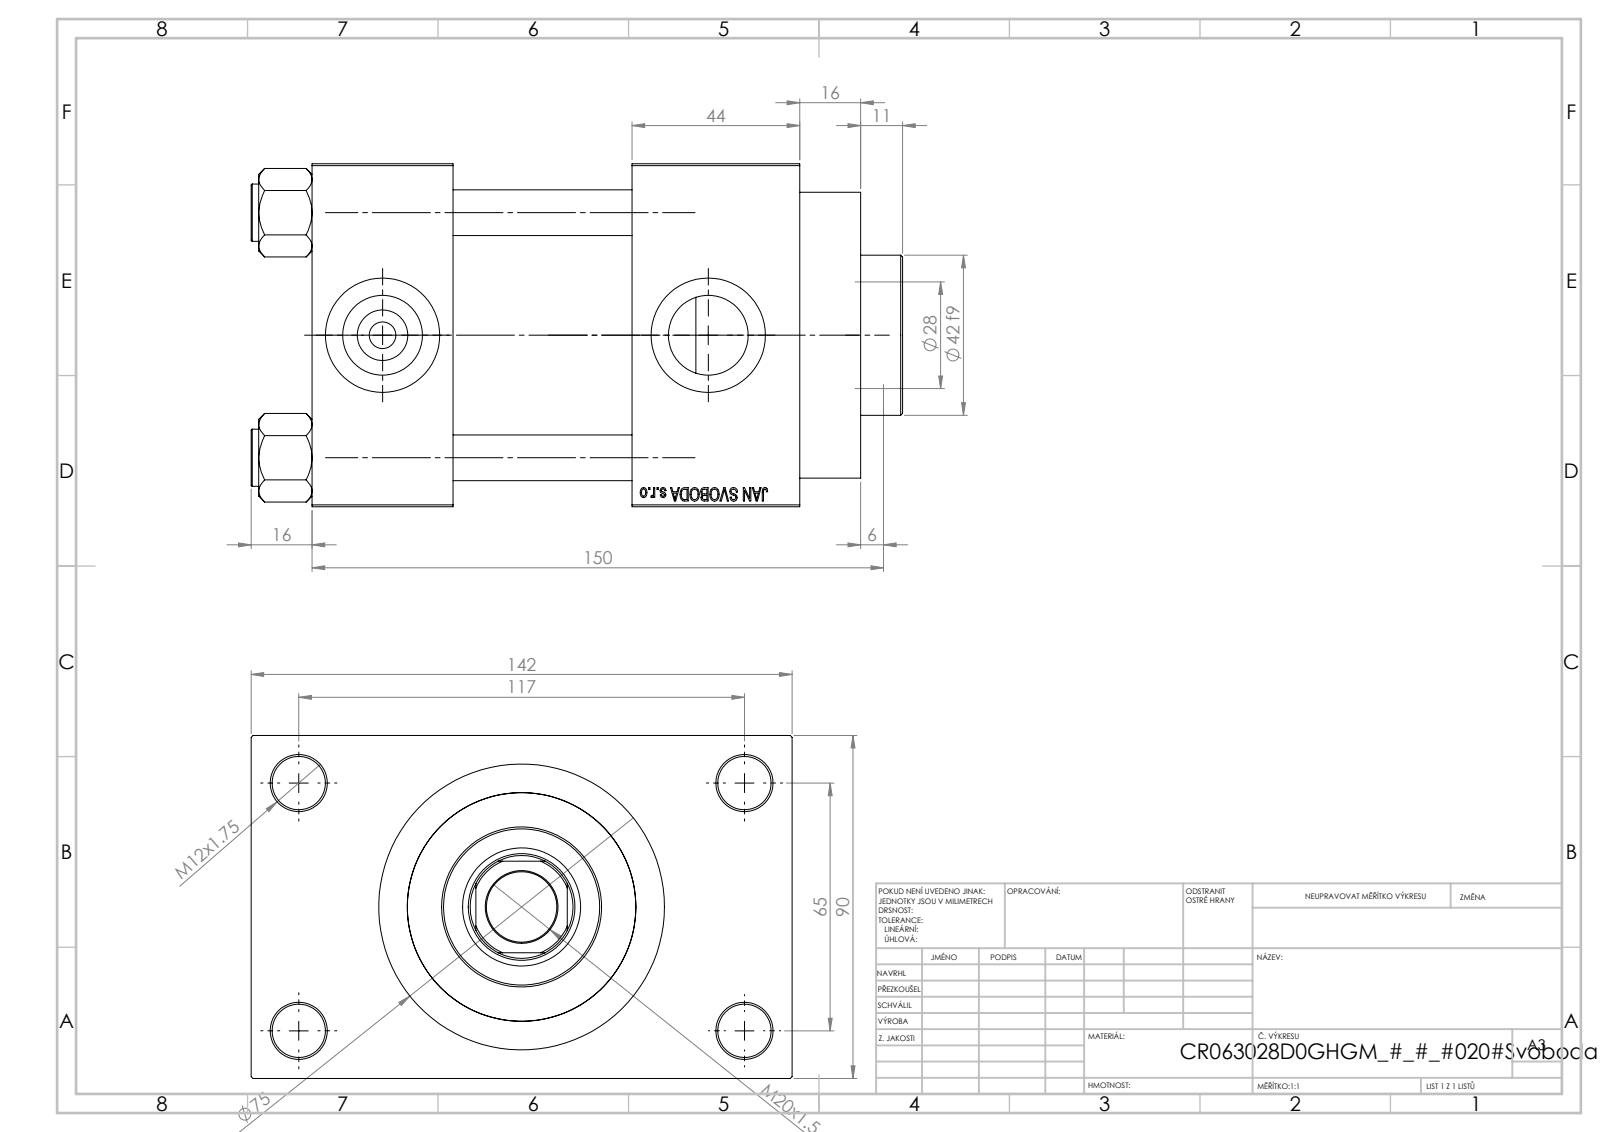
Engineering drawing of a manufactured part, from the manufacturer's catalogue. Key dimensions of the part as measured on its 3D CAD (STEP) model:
Part name (STEP PRODUCT): NUT_M5_D; V215CR_D_TYCINKA; V215CR_D_Body; V215_VC_A (+1 more)
STEP written by: SolidWorks 2019 (CONFIG_CONTROL_DESIGN)
Units: millimetres
Bodies: 11 solids, 1103 faces (497 planar, 88 cylindrical, 518 other)
Overall size (bounding box): 171 × 142 × 90
Volume: 1 021 000 mm³ · Surface area: 186 390 mm²
Round holes (diameter × count): ⌀12 ×4, ⌀14 ×4, ⌀7 ×2, ⌀20.96 ×2, ⌀30 ×2, ⌀18.5 ×1, ⌀28 ×1, ⌀31 ×1, ⌀50 ×1, ⌀60 ×1, ⌀63 ×1
Round bosses / shafts (diameter × count): ⌀15 ×4, ⌀75 ×1, ⌀69 ×1, ⌀42 ×1
Partial cylindrical surfaces — rounded edges, fillets, slot ends (radius × count): R13.5 ×1
Main face-to-face distances: 90, 47, 84, 37, 91, 128, 44, 26, 116, 64
Hole centre spacings: 26.35, 45.47, 64.3, 66.92, 69.81, 90.65, 111.34, 65
